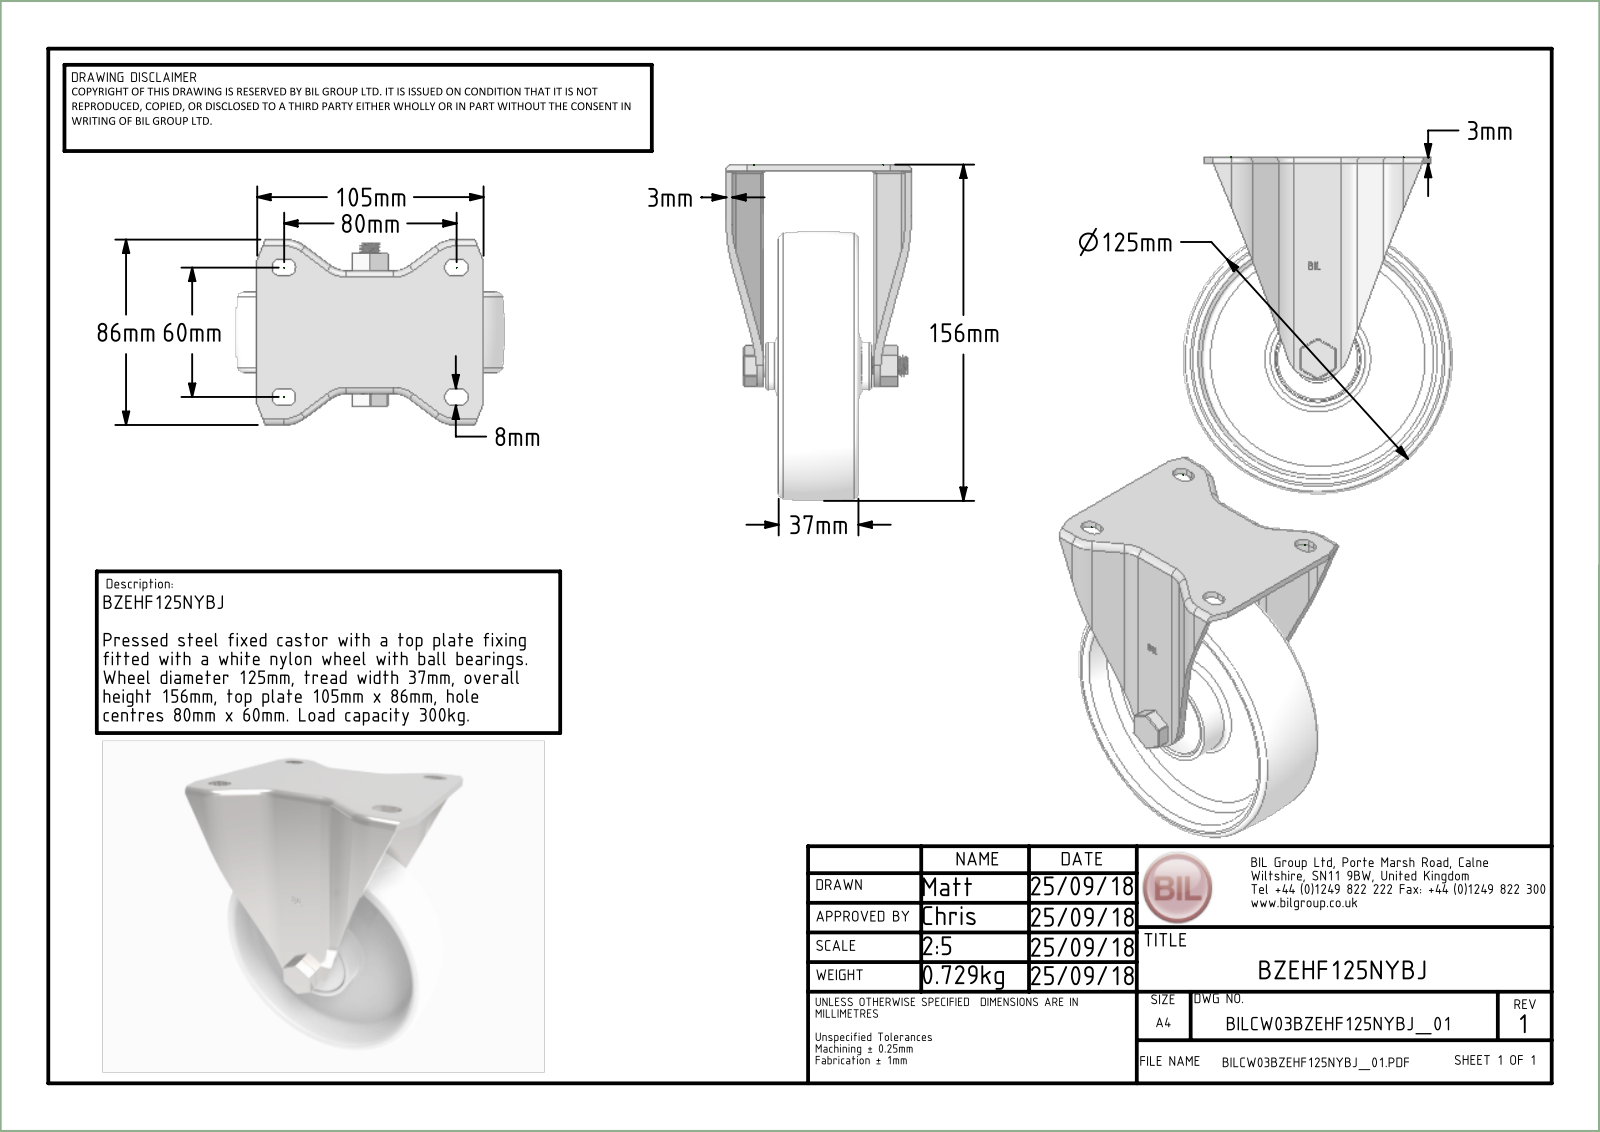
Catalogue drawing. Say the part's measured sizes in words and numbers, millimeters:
The part is named "BZEHF125NYBJ v3; BZHF125AS - 49 v1; ZINC PLATED, PRESSED STEEL BRACKET; BZH125WNYBJM10 v1 (+7 more)". Its 3-D file was written by "Autodesk Translation Framework v14.10.0.0 (AUTOMOTIVE_DESIGN)". It is 20 solids with 741 faces: 282 planar, 185 cylindrical and 274 other. Overall it measures 156 by 125 by 86 millimeters. Its volume is 274 579 cubic millimeters and its surface area 119 059 square millimeters. Round holes: 1 of diameter 10, 1 of diameter 10.2, 1 of diameter 12, 1 of diameter 15, 1 of diameter 20, 1 of diameter 22.5, 1 of diameter 25, 1 of diameter 30, 1 of diameter 31, 1 of diameter 32, 1 of diameter 35, 1 of diameter 36. Round bosses or shafts: 1 of diameter 44, 1 of diameter 38, 1 of diameter 30.5, 1 of diameter 28, 1 of diameter 23, 1 of diameter 19, 1 of diameter 18, 1 of diameter 16. Partial cylindrical surfaces (rounded edges, fillets, slot ends): 18 of radius 0.5, 12 of radius 1.5, 10 of radius 3, 8 of radius 4.5, 6 of radius 0.75, 4 of radius 5, 4 of radius 10, 4 of radius 33.95. The main face-to-face distances are 3, 7, 21, 28, 24, 31, 52, 22.42, 22, 9.
